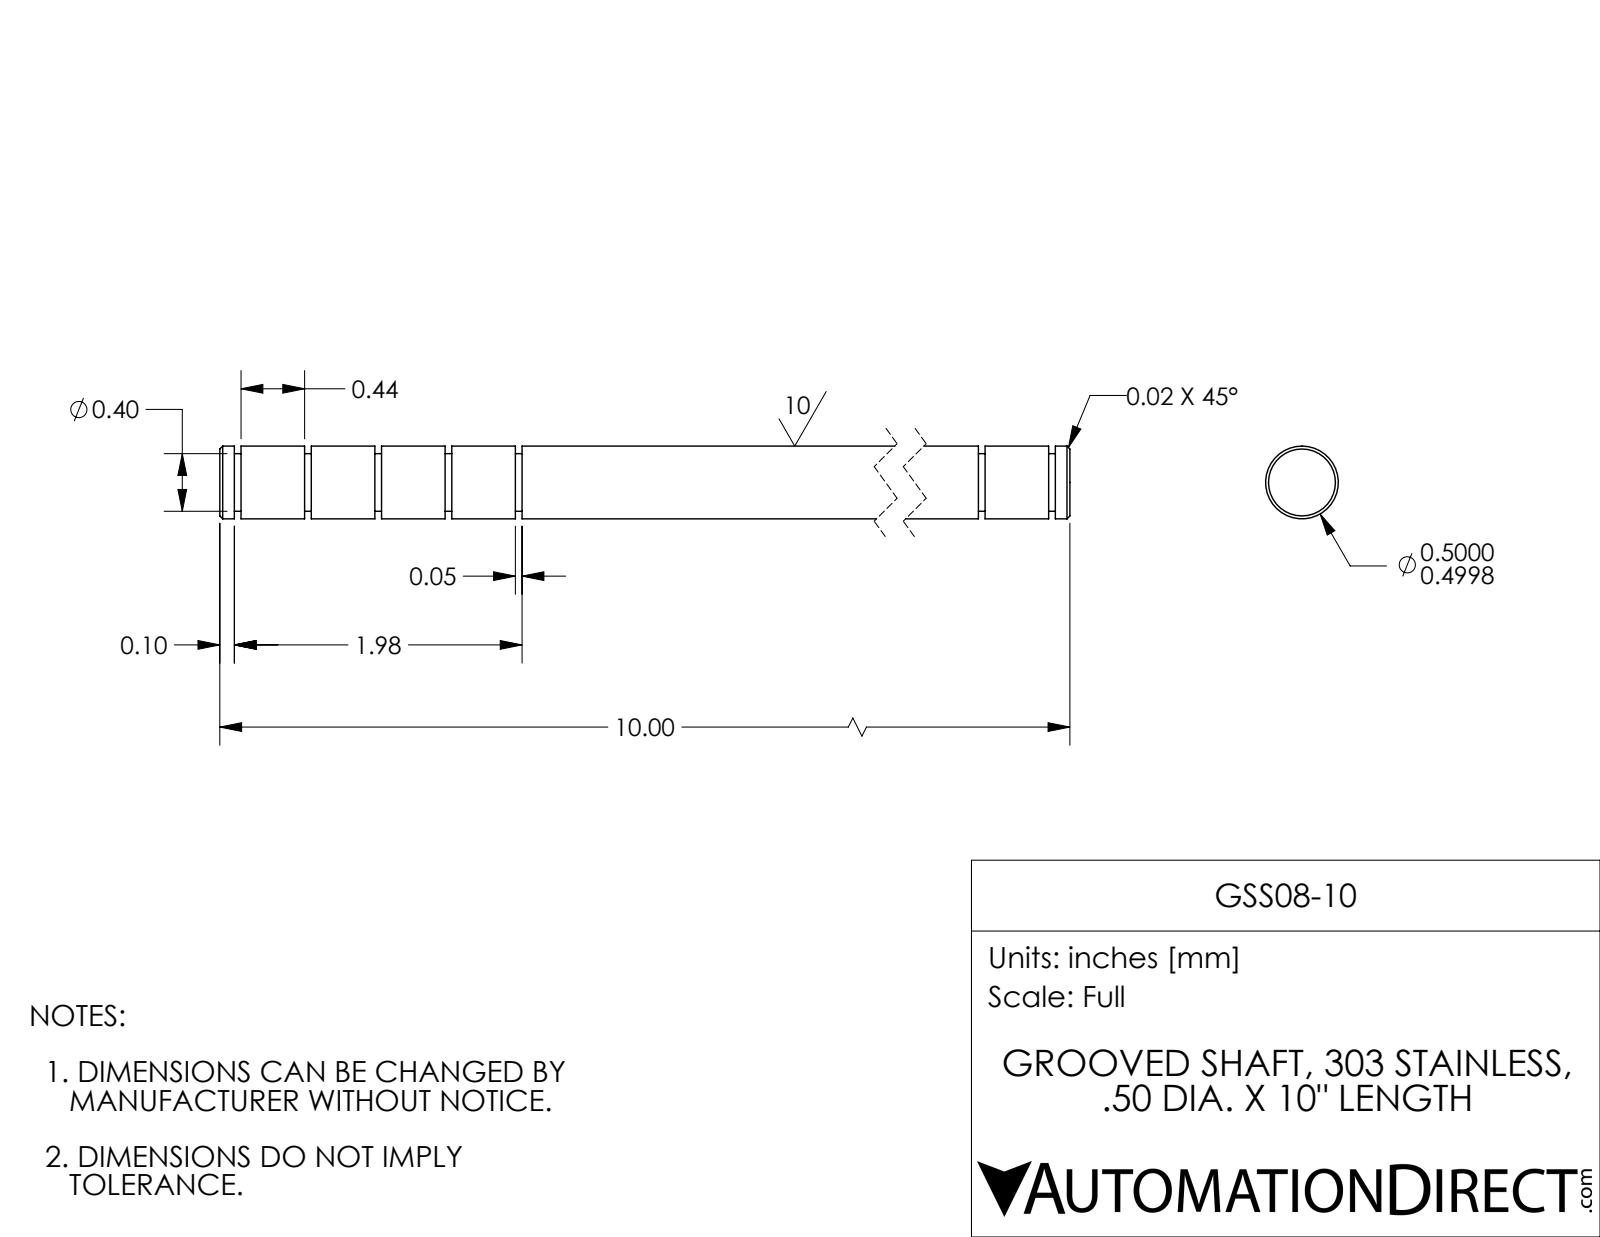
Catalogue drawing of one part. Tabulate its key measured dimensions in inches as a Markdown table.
| quantity | value |
| --- | --- |
| part name | GSS08-10 |
| STEP written by | SolidWorks 2017 (AUTOMOTIVE_DESIGN) |
| units | inches |
| bodies | 1 solid, 50 faces (16 planar, 30 cylindrical, 4 other) |
| overall size | 10 × 0.5 × 0.5 |
| volume | 1.939 in³ |
| surface area | 16.98 in² |
| round bosses / shafts (diameter × count) | 0.5 × 1, 0.396 × 1 |
| main face-to-face distances | 0.483, 0.046, 0.437, 1.449, 9.271, 7.822, 0.966, 0.529, 1.012, 8.788 |
